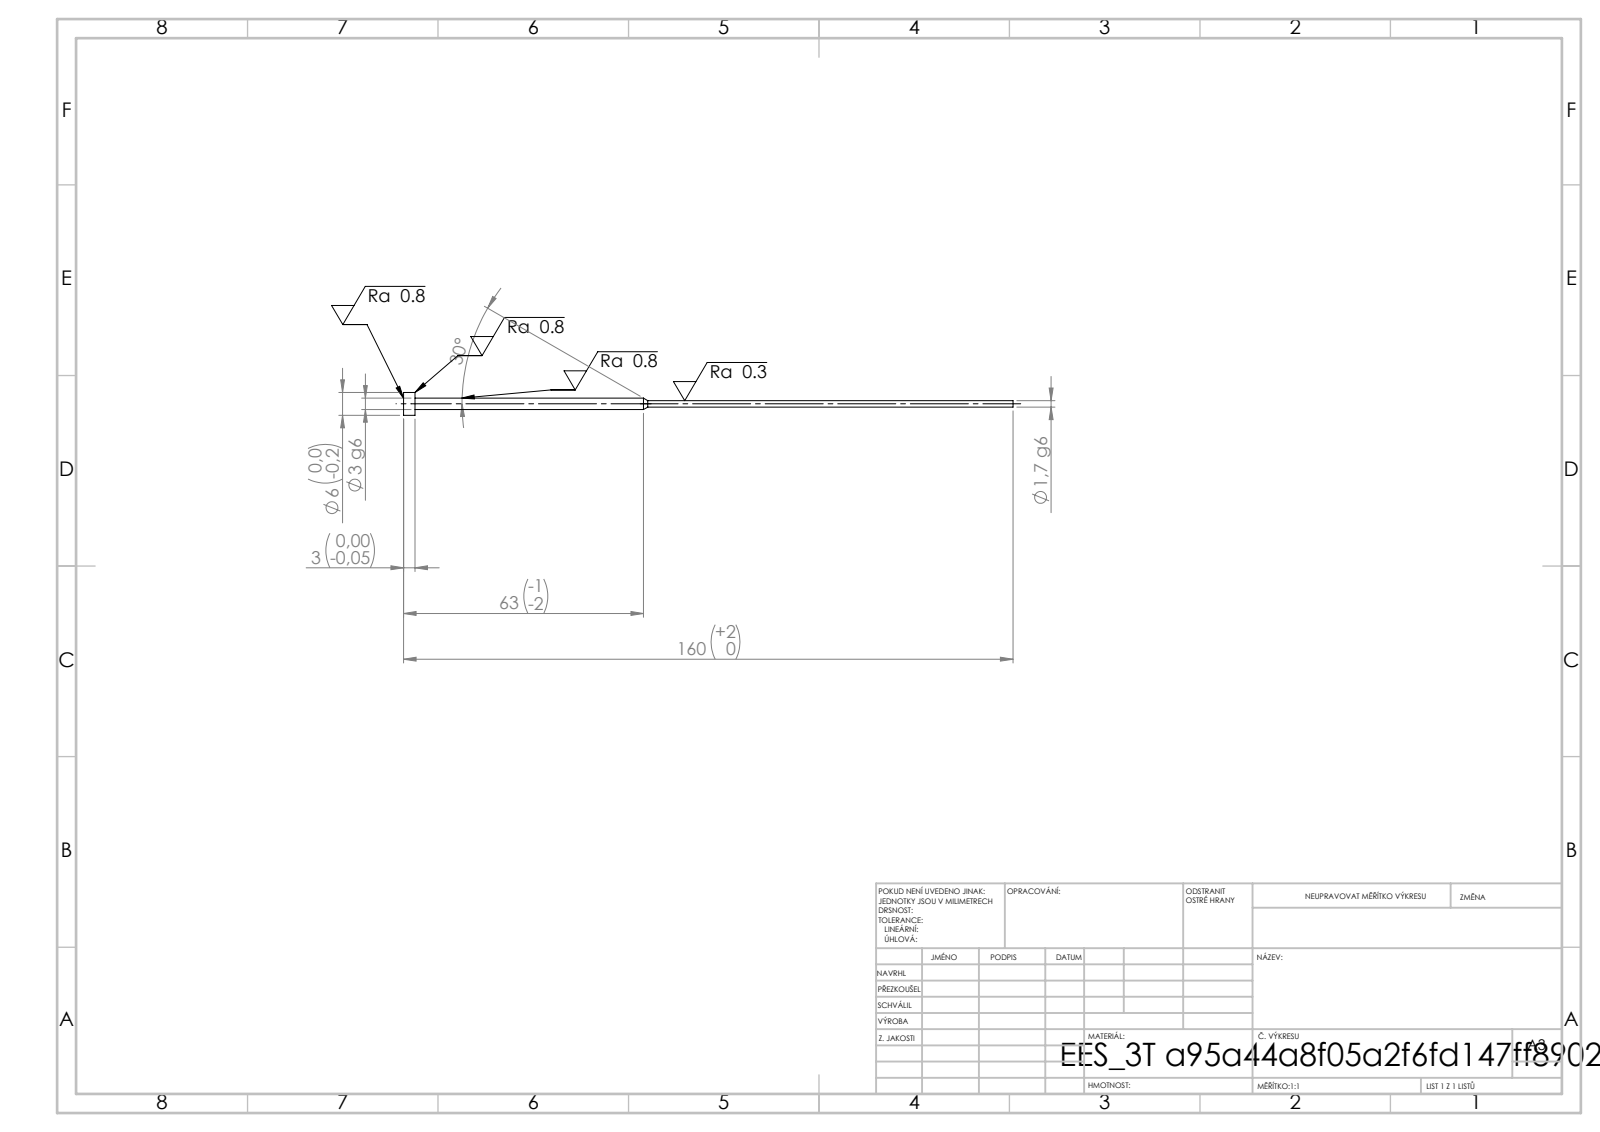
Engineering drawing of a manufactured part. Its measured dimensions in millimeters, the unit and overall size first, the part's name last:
Units: millimetres
Overall size (bounding box): 160 × 6 × 6
Round bosses / shafts (diameter × count): ⌀6 ×1, ⌀3 ×1, ⌀1.7 ×1
Main face-to-face distances: 3, 157, 160
Volume: 732 mm³ · Surface area: 1 195 mm²
Bodies: 1 solid, 11 faces (3 planar, 6 cylindrical, 2 other)
STEP written by: SolidWorks 2019 (CONFIG_CONTROL_DESIGN)
